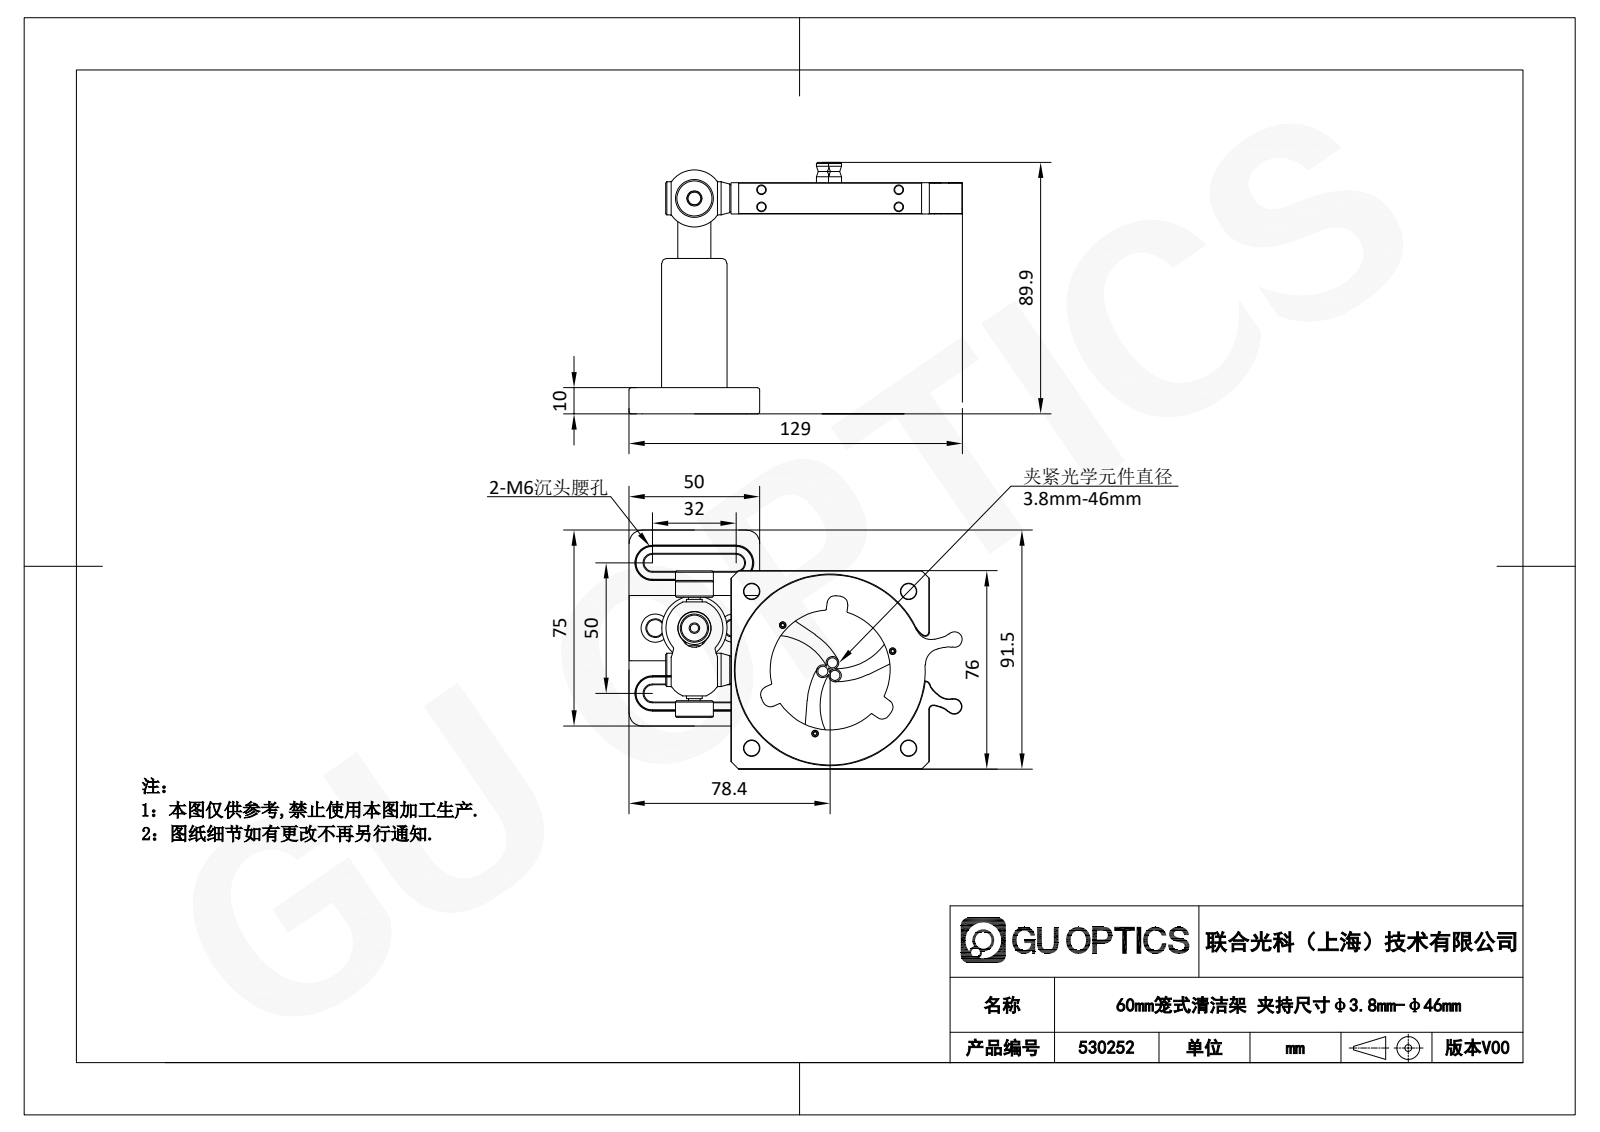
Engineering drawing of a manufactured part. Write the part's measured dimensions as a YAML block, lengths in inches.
part_name: "530252; PH-75A-1-3-1-SH_1-2________________.step; 3.03.01.03.051_M2.0×5_内六角平圆头螺钉_碳钢黑色; 3.03.01.07.026_平端紧定螺钉M3×3 (+8 more)"
step_written_by: "SolidWorks 2020 (CONFIG_CONTROL_DESIGN)"
units: inches
bodies: {solids: 45, faces: 916, planar: 387, cylindrical: 224, other: 305}
overall_size: [5.151, 4.546, 3.809]
volume: 6.495
surface_area: 97.38
round_holes:
  - {diameter: 0.063, count: 15}
  - {diameter: 0.13, count: 10}
  - {diameter: 0.197, count: 5}
  - {diameter: 0.094, count: 4}
  - {diameter: 0.169, count: 4}
  - {diameter: 0.236, count: 4}
  - {diameter: 0.098, count: 3}
  - {diameter: 0.193, count: 3}
  - {diameter: 0.26, count: 3}
  - {diameter: 0.433, count: 3}
  - {diameter: 0.126, count: 2}
  - {diameter: 0.157, count: 2}
round_bosses_or_shafts:
  - {diameter: 0.079, count: 9}
  - {diameter: 0.571, count: 3}
  - {diameter: 0.197, count: 3}
  - {diameter: 0.118, count: 3}
  - {diameter: 0.499, count: 2}
  - {diameter: 0.236, count: 2}
  - {diameter: 0.177, count: 2}
  - {diameter: 0.984, count: 1}
partial_cylinders:
  - {radius: 0.118, count: 16}
  - {radius: 0.008, count: 10}
  - {radius: 0.031, count: 10}
  - {radius: 0.236, count: 6}
  - {radius: 0.197, count: 5}
  - {radius: 0.059, count: 4}
  - {radius: 0.13, count: 4}
  - {radius: 0.256, count: 4}
face_to_face_distances: [0.394, 0.079, 3.03, 3.109, 0.472, 0.315, 2.636, 2.715, 3.424, 3.502]
hole_center_spacings: [0.256, 1.043, 1.396, 1.02, 1.67, 1.807, 2.071, 2.087]
